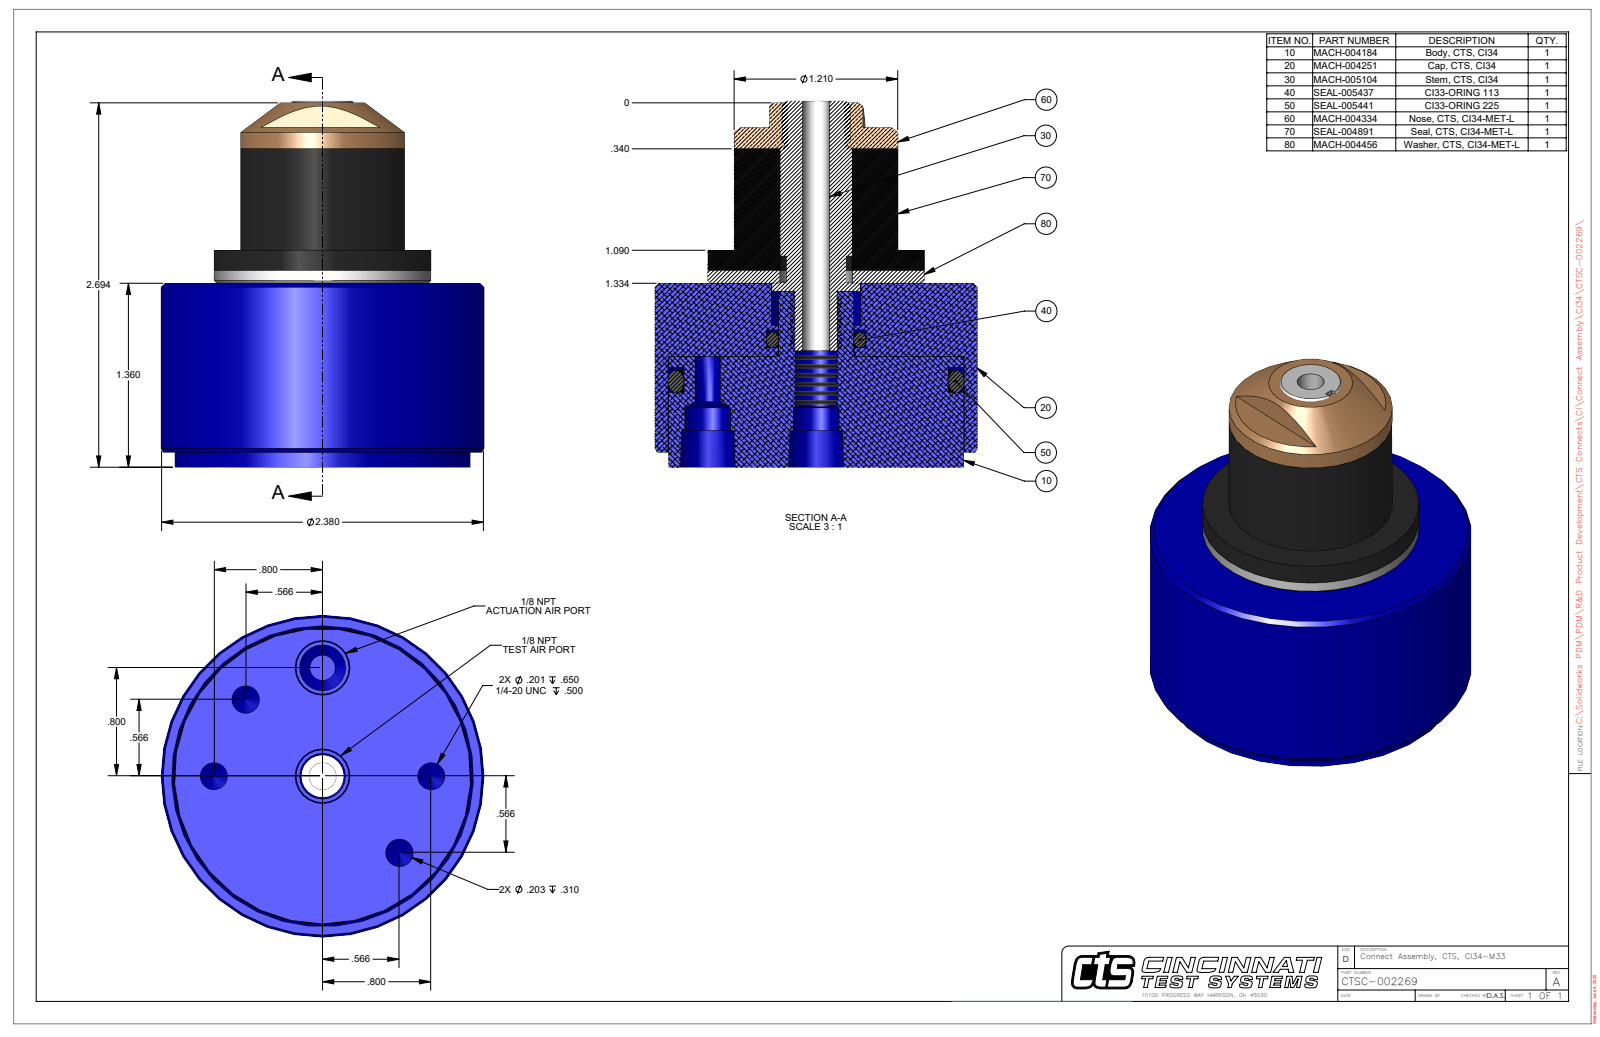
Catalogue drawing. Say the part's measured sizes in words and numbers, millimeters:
The part is named "CTSC-002269". Its 3-D file was written by "SolidWorks 2023 (AUTOMOTIVE_DESIGN)". It is 1 solid with 77 faces: 23 planar, 29 cylindrical and 25 other. Overall it measures 68.7 by 60.5 by 60.5 millimeters. Its volume is 120 500 cubic millimeters and its surface area 20 520 square millimeters. Round holes: 2 of diameter 5.1, 2 of diameter 5.2, 2 of diameter 8.6, 1 of diameter 5.2, 1 of diameter 16.8, 1 of diameter 55.6. Round bosses or shafts: 1 of diameter 60.5, 1 of diameter 55.3, 1 of diameter 40.6, 1 of diameter 30.7, 1 of diameter 16.5. Partial cylindrical surfaces (rounded edges, fillets, slot ends): 1 of radius 5.4. The main face-to-face distances are 34.5, 40.7, 6.2, 2.8, 31.8, 37.9, 63.8, 61, 29.2, 23. The hole center spacings are 20.3, 15.5, 37.5, 28.7, 40.6.
